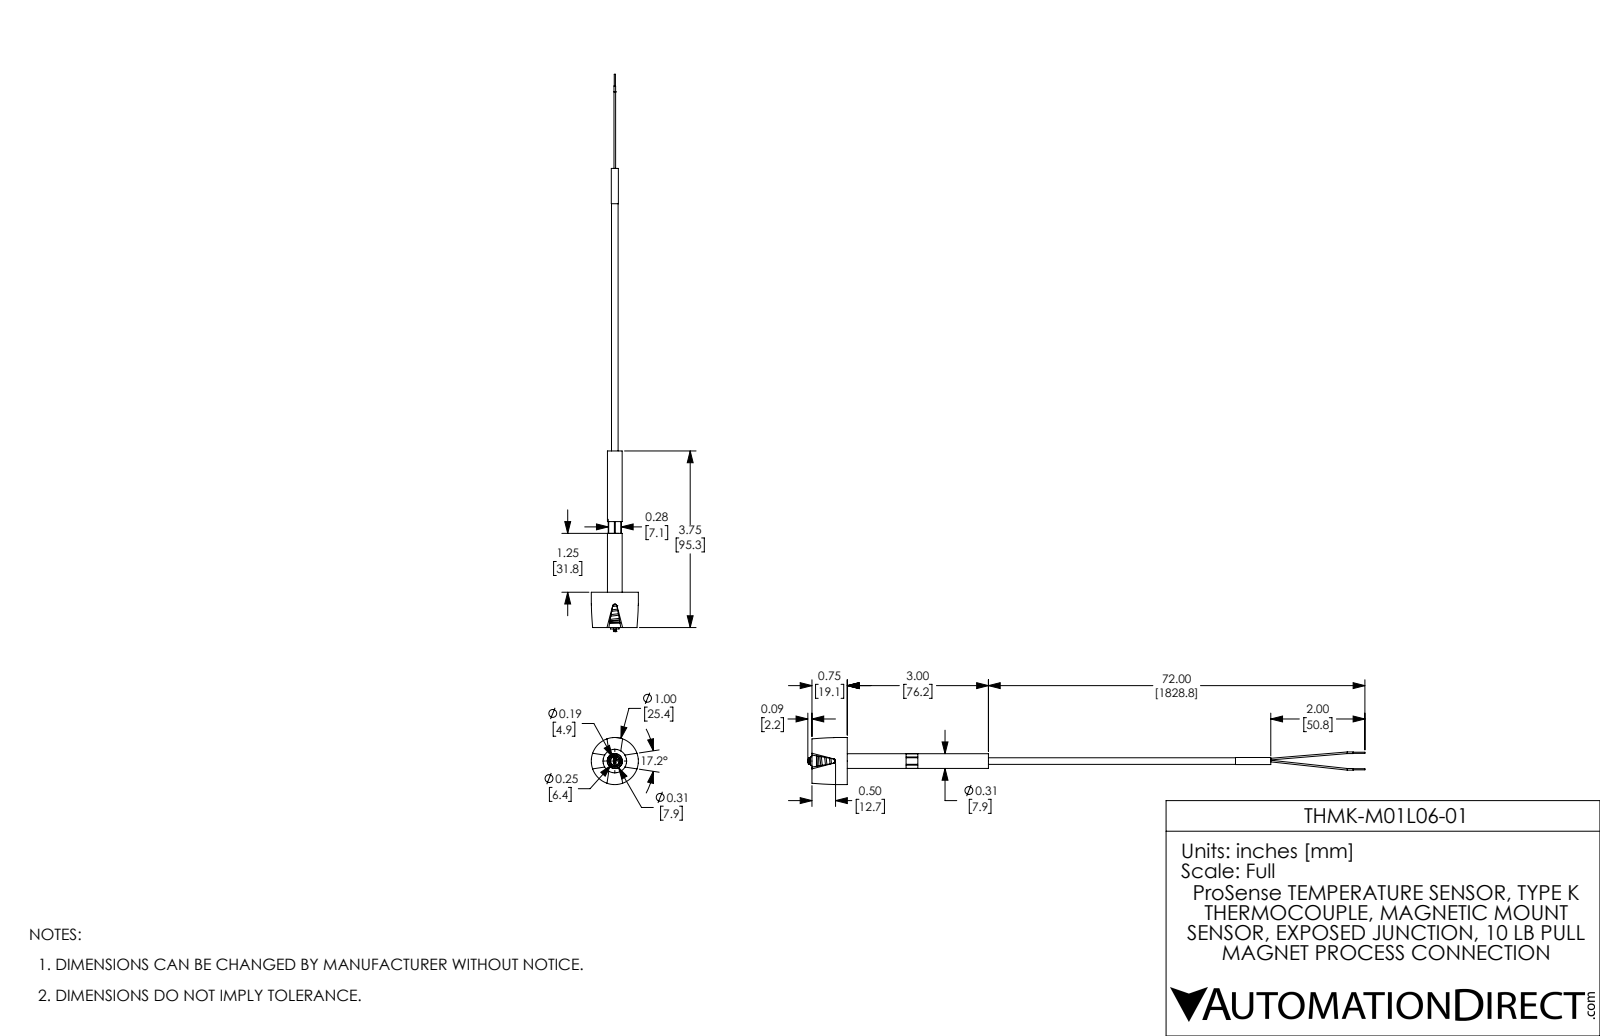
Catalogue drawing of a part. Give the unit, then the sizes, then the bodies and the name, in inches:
Units: inches
Overall size (bounding box): 11.839 × 1 × 1
Round holes (diameter × count): ⌀0.194 ×1, ⌀0.253 ×1, ⌀0.26 ×1, ⌀0.5 ×1
Round bosses / shafts (diameter × count): ⌀0.035 ×4, ⌀0.025 ×2, ⌀1 ×1, ⌀0.313 ×1, ⌀0.25 ×1, ⌀0.181 ×1, ⌀0.15 ×1, ⌀0.14 ×1
Main face-to-face distances: 0.75, 0.25, 0.5, 0.28, 3.25, 3, 3.75, 1.5, 3.655, 0.655
Volume: 0.754 in³ · Surface area: 13.68 in²
Bodies: 8 solids, 114 faces (46 planar, 36 cylindrical, 32 other)
Part name (STEP PRODUCT): THMJ-M01L06-02
STEP written by: SolidWorks 2017 (AUTOMOTIVE_DESIGN)
